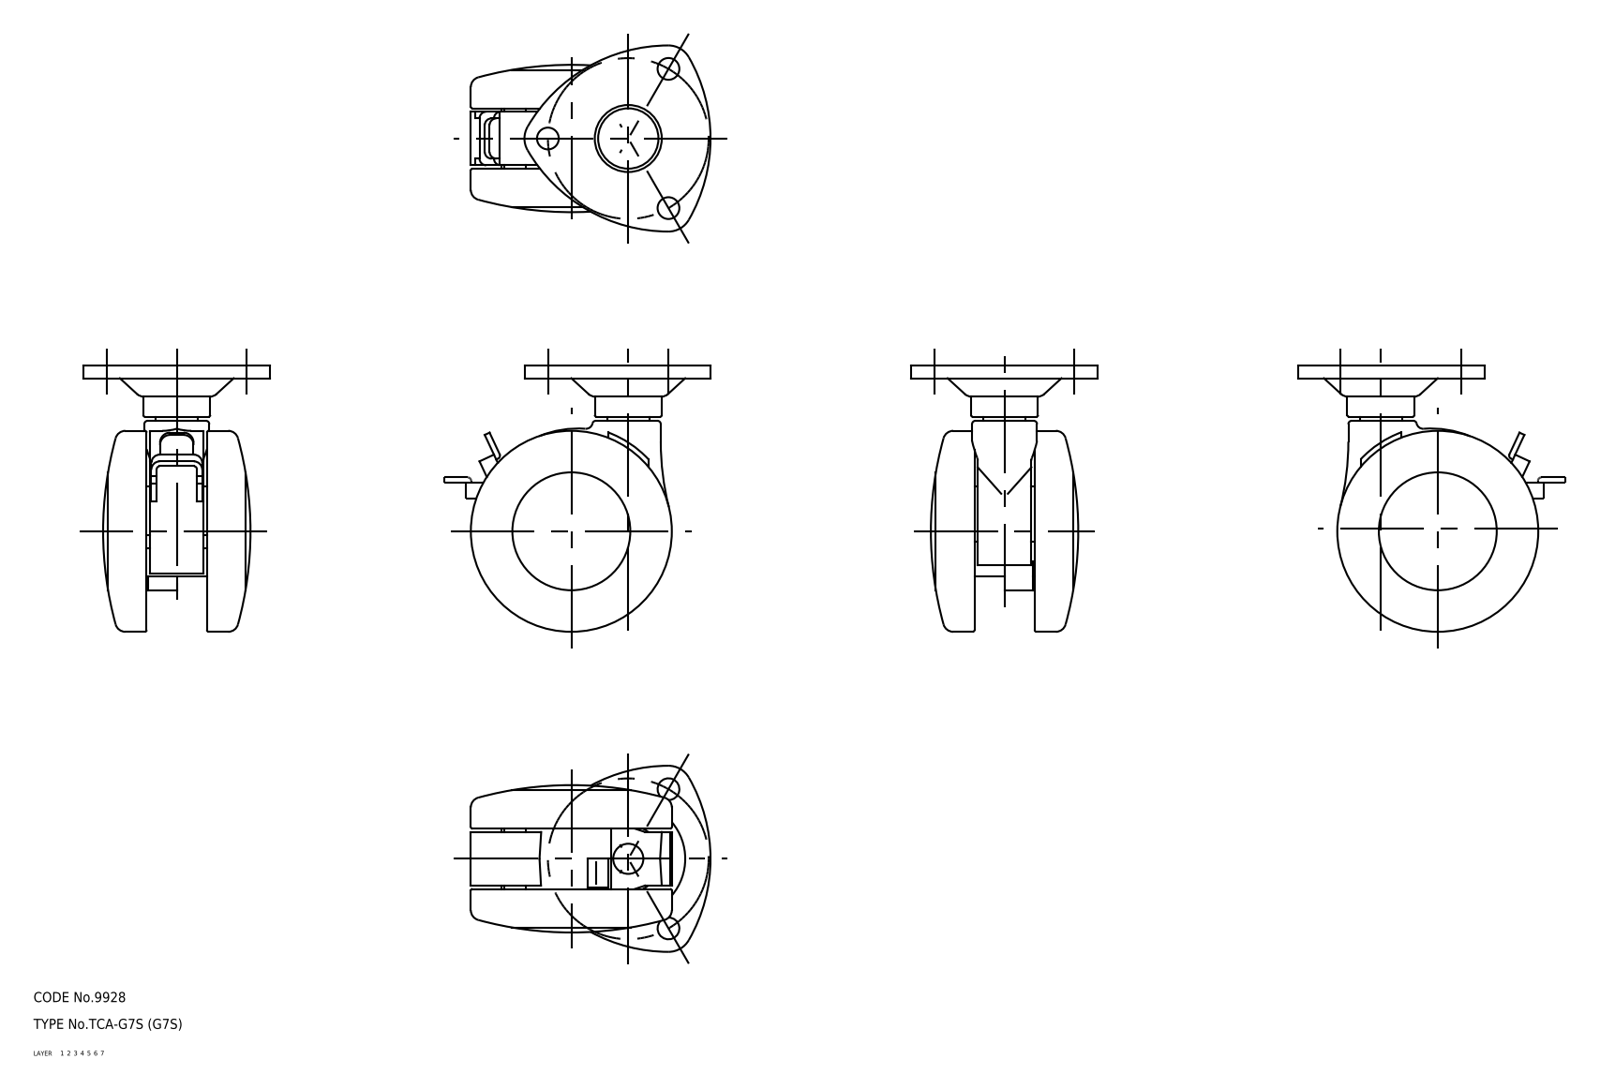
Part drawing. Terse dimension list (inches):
name: wheel; mounting plate; main shaft; lever (+1 more)
written by: CADfix (AUTOMOTIVE_DESIGN)
unit: in
bodies: 6 solids, 216 faces (0 planar, 0 cylindrical, 216 other)
size: 3.132 × 3.13 × 2.188
volume: 6.224 in³; area: 61.98 in²
